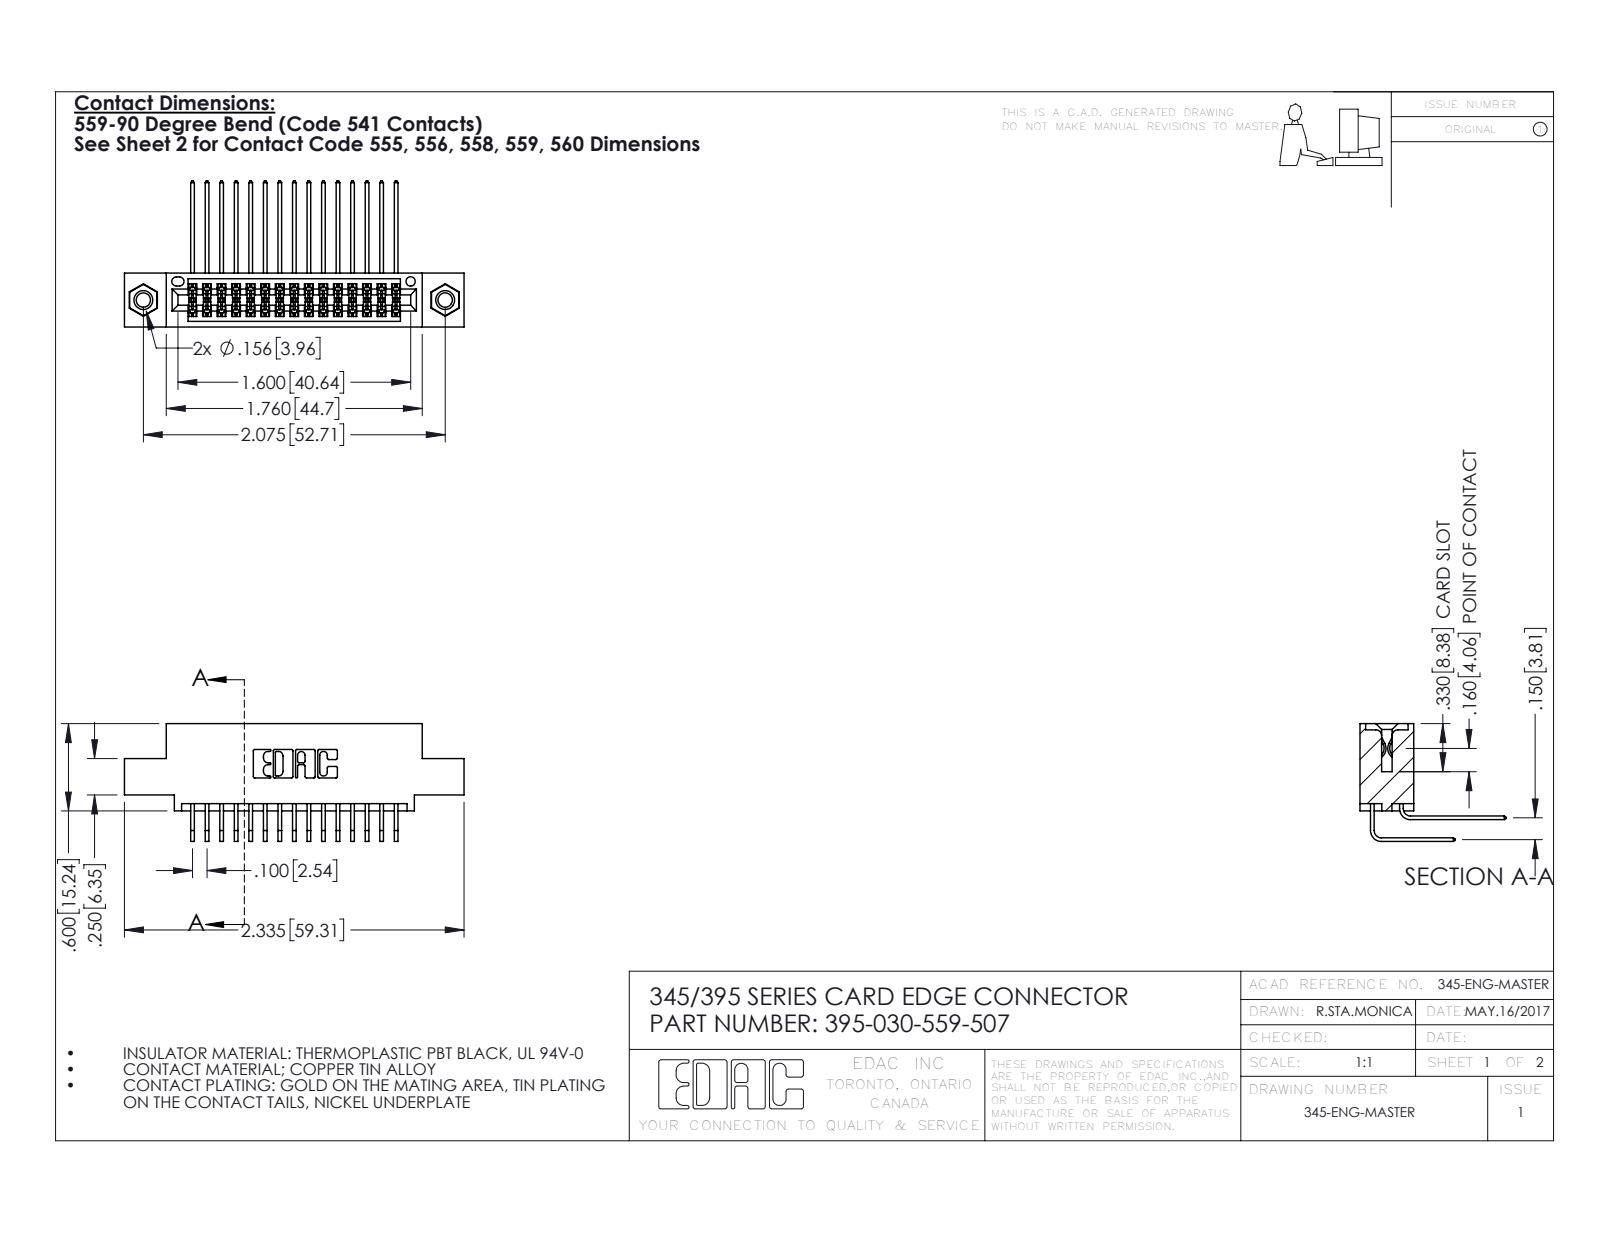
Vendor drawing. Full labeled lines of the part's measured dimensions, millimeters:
Part name (STEP PRODUCT): 345-292-001_559 Tail - 2; 345-292-001_558 559 Tail - 1; 395-030-559-507; 345 Part_0.110 Offset - 0.156 Dia-TI (+1 more)
STEP written by: SolidWorks 2016 (CONFIG_CONTROL_DESIGN)
Units: millimetres
Bodies: 33 solids, 1750 faces (1166 planar, 568 cylindrical, 16 other)
Overall size (bounding box): 59.3 × 25.5 × 20.5
Volume: 5 600 mm³ · Surface area: 8 684 mm²
Round holes (diameter × count): ⌀2.5 ×2, ⌀3.2 ×2, ⌀4 ×2, ⌀1.6 ×1
Round bosses / shafts (diameter × count): ⌀3.9 ×2
Partial cylindrical surfaces — rounded edges, fillets, slot ends (radius × count): R0.2 ×45, R0.3 ×22, R0.2 ×6, R0.8 ×6, R0.7 ×3, R0.4 ×2, R0.5 ×2, R0.6 ×2
Main face-to-face distances: 1.8, 7.6, 5.1, 9.4, 2.5, 6.9, 0.6, 5.7, 3.8, 4.4
Hole centre spacings: 6.9, 46.8, 52.7
